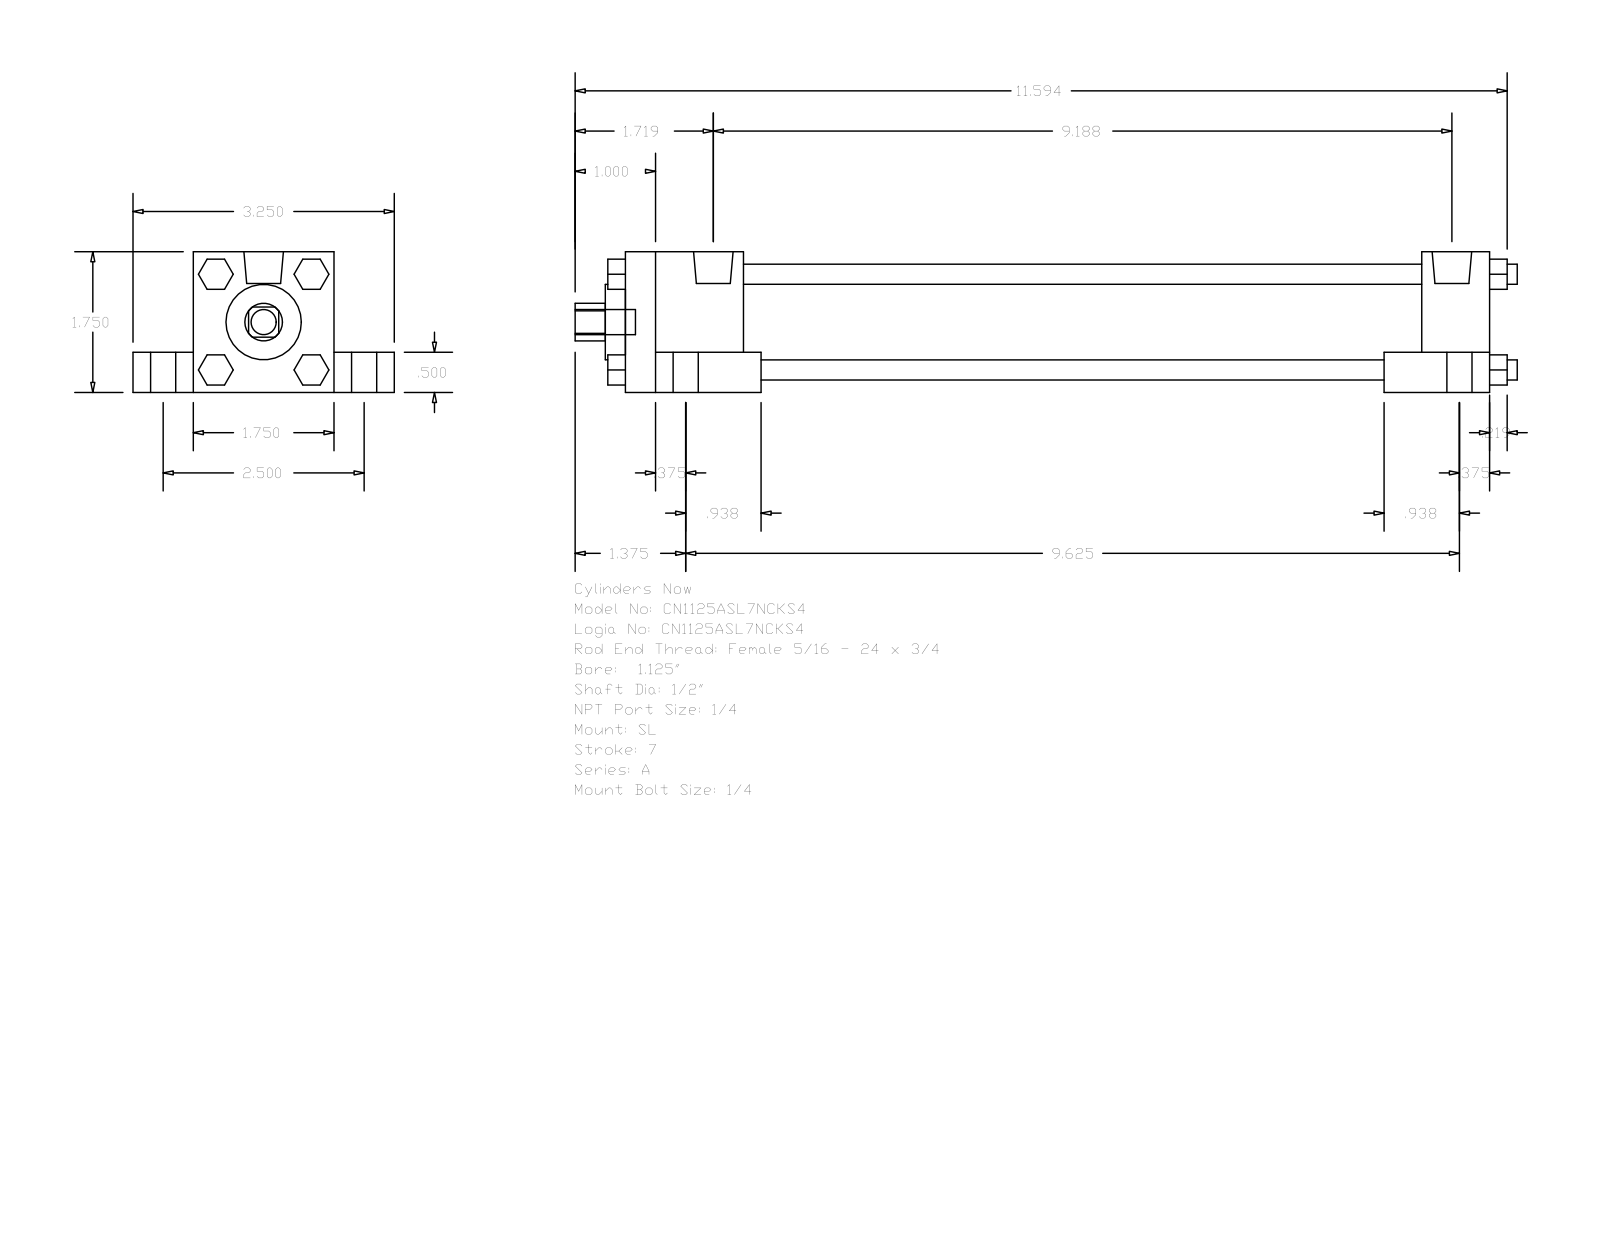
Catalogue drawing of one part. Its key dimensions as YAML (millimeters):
part_name: "A_SL__0112_0.5"
step_written_by: "GSSL Pune (CONFIG_CONTROL_DESIGN)"
units: millimeters
bodies: {solids: 0, faces: 150, planar: 114, cylindrical: 36, other: 0}
overall_size: [297.66, 82.55, 44.45]
round_holes:
  - {diameter: 12.7, count: 1}
  - {diameter: 23.81, count: 1}
  - {diameter: 31.88, count: 1}
round_bosses_or_shafts:
  - {diameter: 7.94, count: 5}
  - {diameter: 14.29, count: 4}
  - {diameter: 6.35, count: 4}
  - {diameter: 5.56, count: 4}
  - {diameter: 12.49, count: 2}
partial_cylinders:
  - {radius: 5.94, count: 1}
face_to_face_distances: [44.46, 31.76, 12.7, 19.04, 63.5, 273.05, 251.61, 21.44, 37.3, 214.31]
